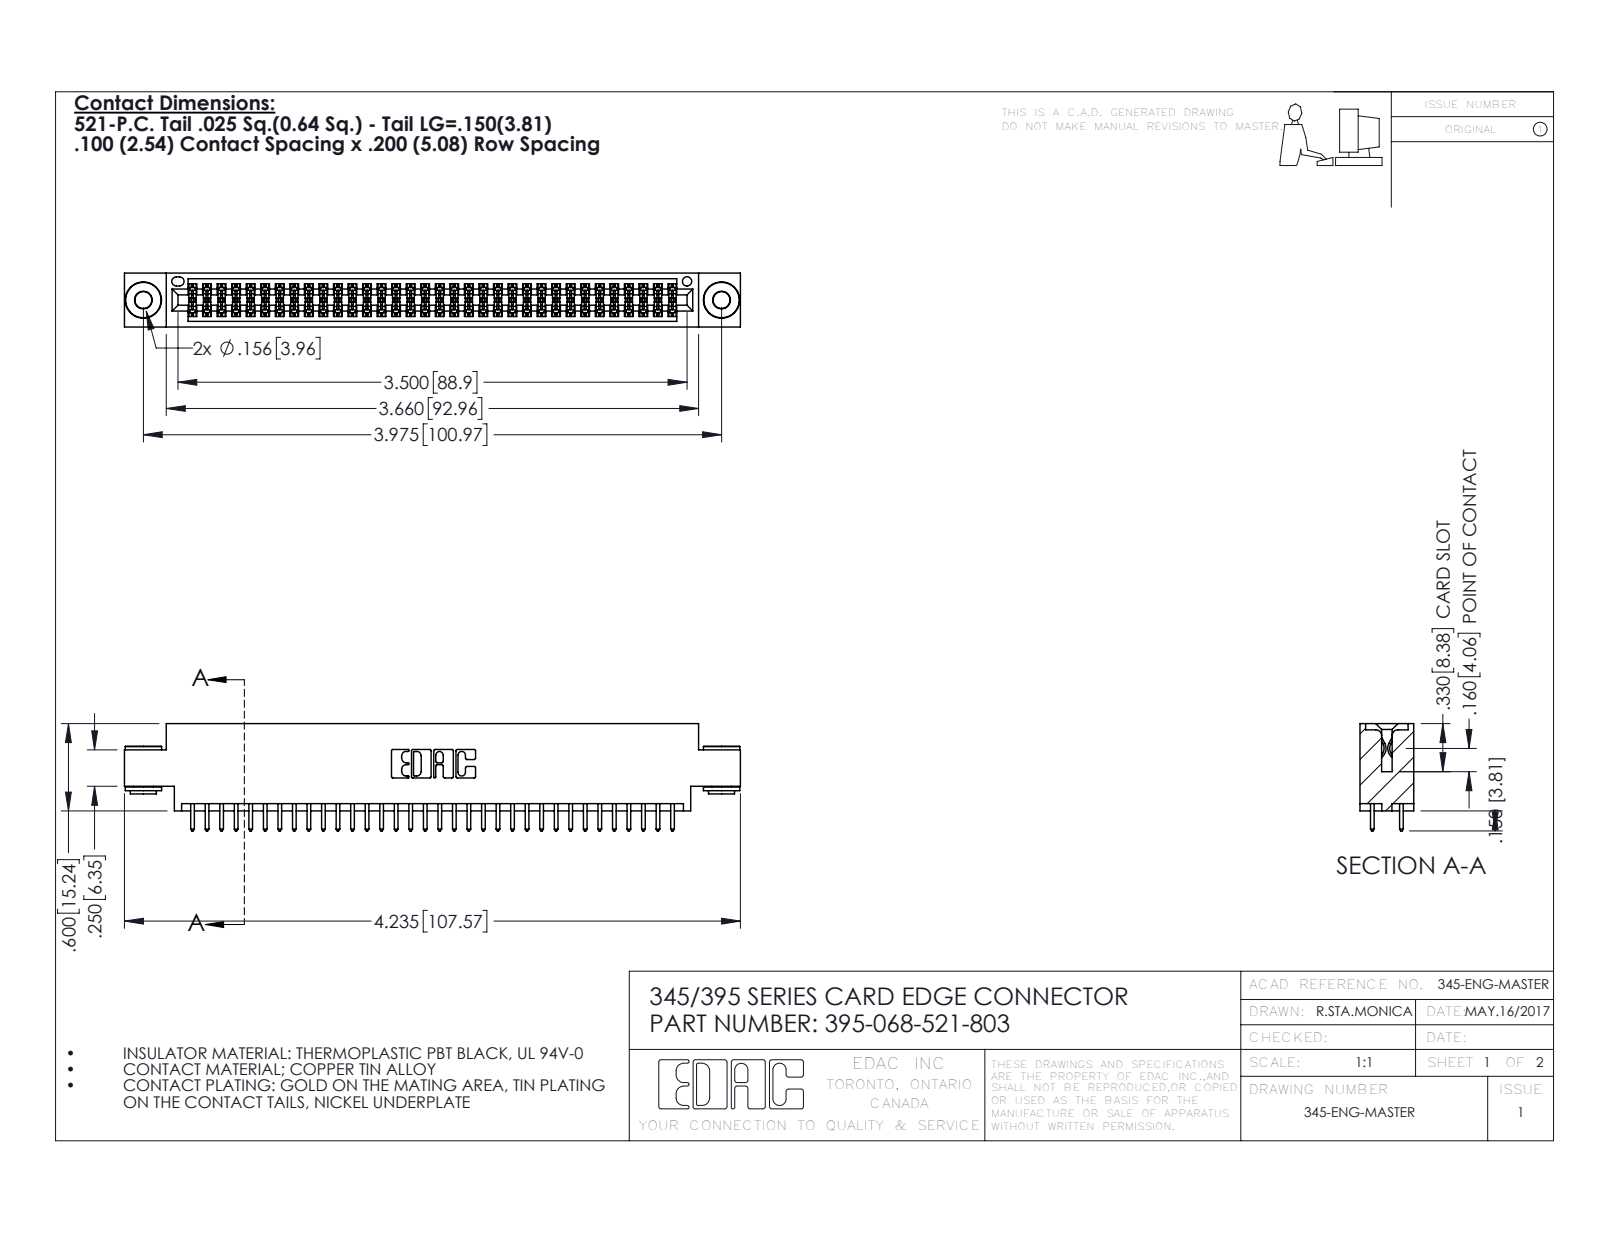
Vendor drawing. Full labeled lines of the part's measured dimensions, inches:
Part name (STEP PRODUCT): 345-292-001_345-293-121; 345-250-002_345-250-002-102; 345 Part_0.170 Offset - 0.156 Dia-TH; 395-068-521-803
STEP written by: SolidWorks 2016 (CONFIG_CONTROL_DESIGN)
Units: inches
Bodies: 71 solids, 3568 faces (2338 planar, 1222 cylindrical, 8 other)
Overall size (bounding box): 4.235 × 0.737 × 0.37
Volume: 0.626 in³ · Surface area: 23.51 in²
Round holes (diameter × count): ⌀0.116 ×2, ⌀0.156 ×2, ⌀0.064 ×1
Round bosses / shafts (diameter × count): ⌀0.25 ×2, ⌀0.18 ×2, ⌀0.136 ×2
Partial cylindrical surfaces — rounded edges, fillets, slot ends (radius × count): R0.006 ×102, R0.01 ×68, R0.01 ×22, R0.007 ×6, R0.031 ×6, R0.026 ×3, R0.014 ×2, R0.019 ×2
Main face-to-face distances: 0.072, 0.298, 0.37, 0.2, 0.098, 0.272, 0.025, 0.225, 0.175, 0.149
Hole centre spacings: 0.27, 3.74, 3.975
